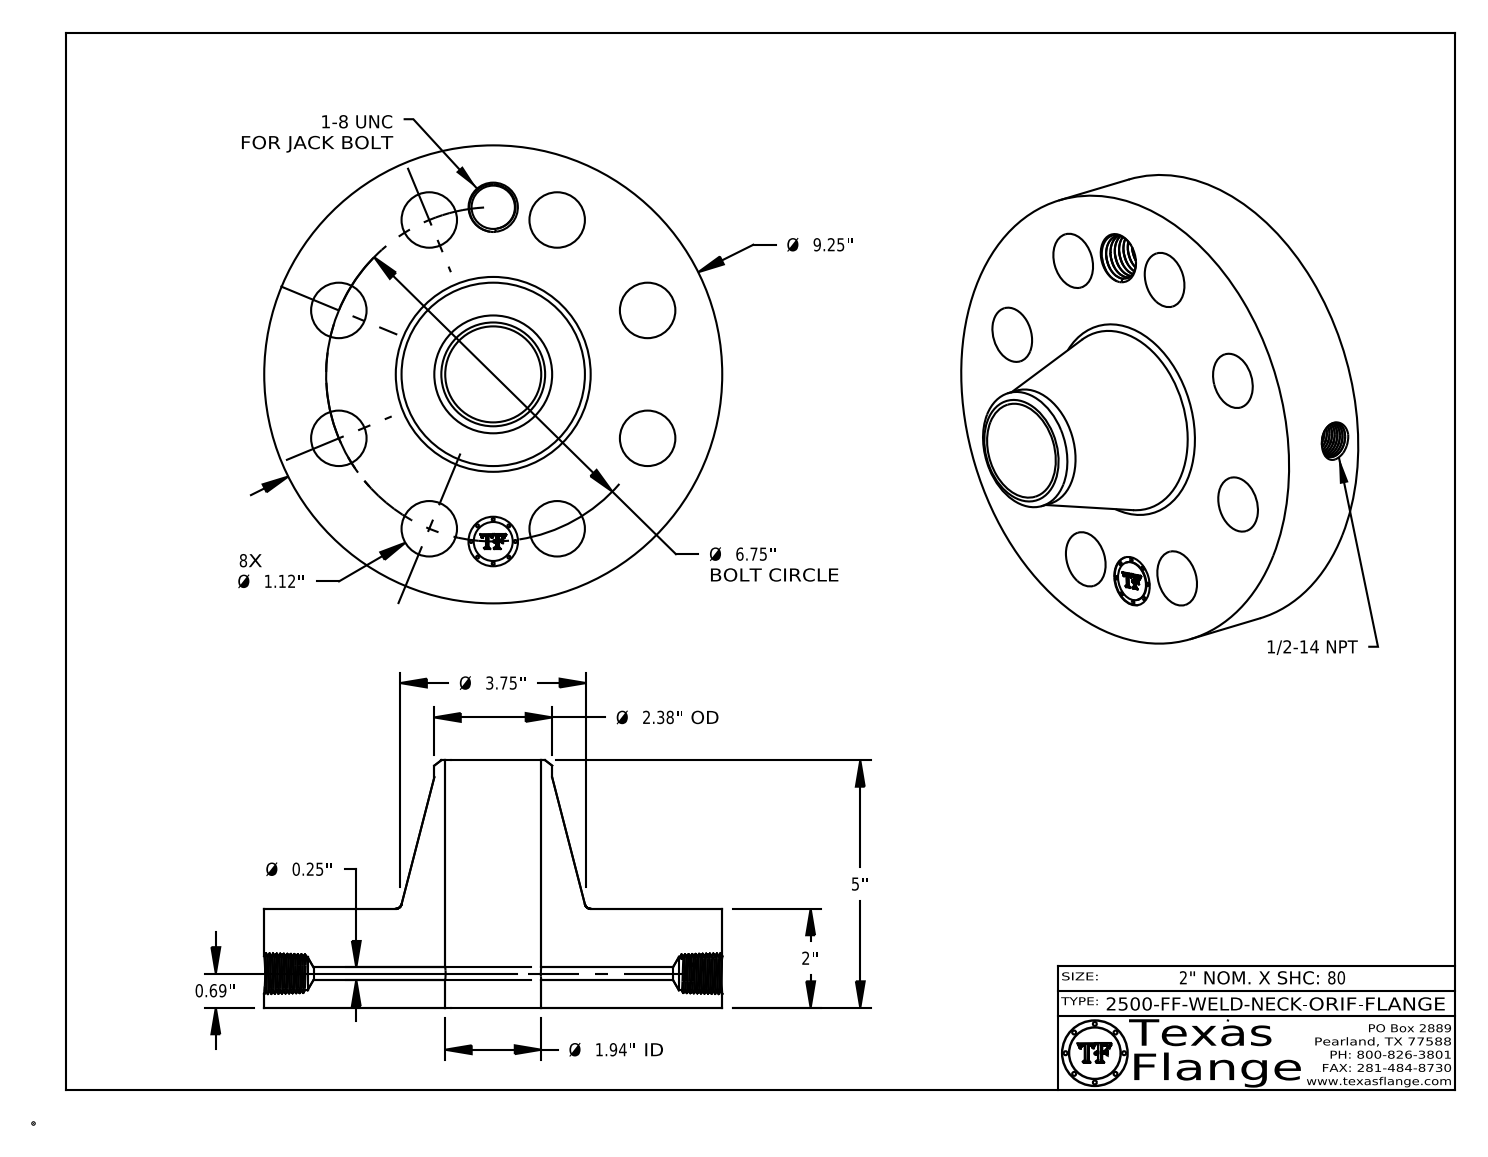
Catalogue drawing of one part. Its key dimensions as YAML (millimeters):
part_name: "2500-FF-WELD-NECK"
step_written_by: "CATIA V5 STEP AP214 (AUTOMOTIVE_DESIGN)"
units: millimeters
bodies: {solids: 1, faces: 775, planar: 368, cylindrical: 93, other: 314}
overall_size: [235, 235, 127]
volume: 2014000
surface_area: 191700
round_holes:
  - {diameter: 28.4, count: 8}
  - {diameter: 6.4, count: 1}
  - {diameter: 17.1, count: 1}
  - {diameter: 22.2, count: 1}
  - {diameter: 25.4, count: 1}
  - {diameter: 49.3, count: 1}
round_bosses_or_shafts:
  - {diameter: 1.5, count: 8}
  - {diameter: 235, count: 1}
  - {diameter: 60.5, count: 1}
  - {diameter: 20, count: 1}
face_to_face_distances: [50.8, 127, 76.2, 0.4, 50.4, 76.6, 7.6, 7.4, 1.4, 6.3]
hole_center_spacings: [85.7, 121.2, 33.5, 65.6, 65.6, 95.3, 142.6, 158.4]
